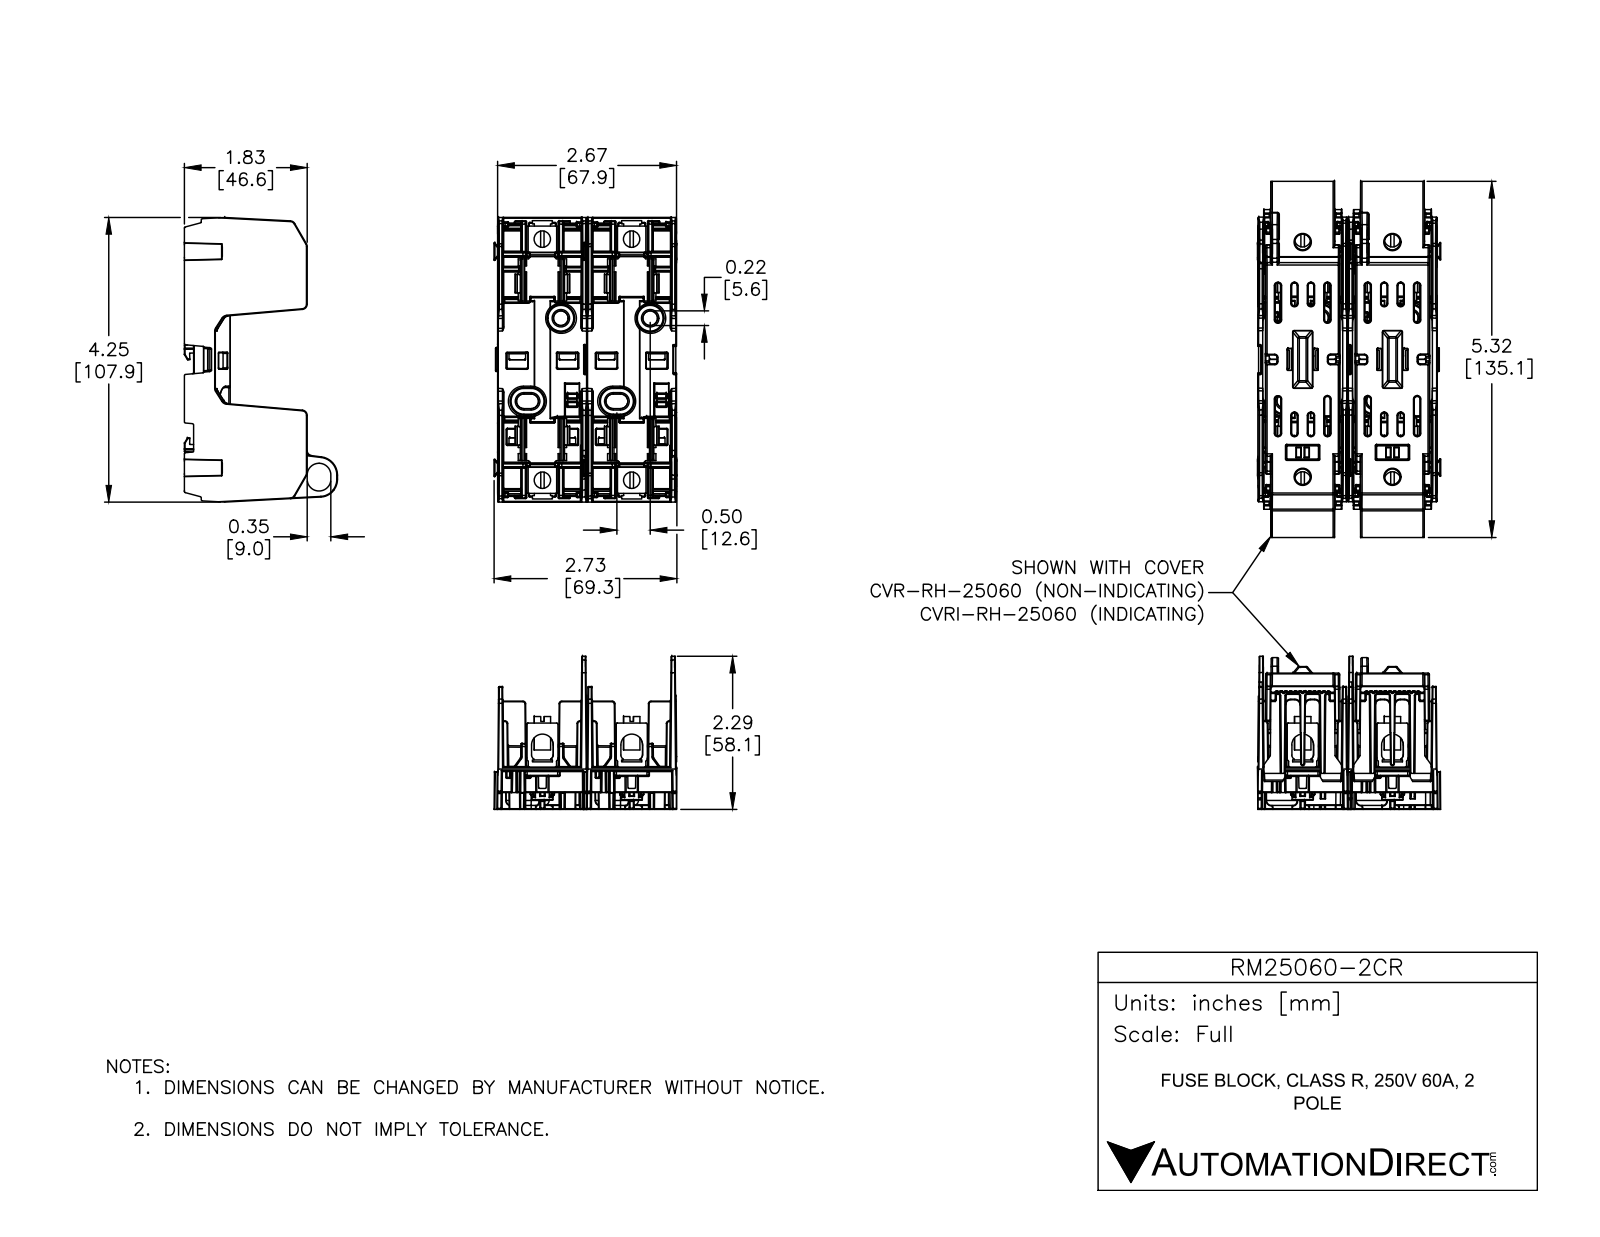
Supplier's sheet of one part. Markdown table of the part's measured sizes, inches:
| quantity | value |
| --- | --- |
| part name | RM25060-1CR; RM25060-2CR |
| STEP written by | SolidWorks 2016 (AUTOMOTIVE_DESIGN) |
| units | inches |
| bodies | 26 solids, 788 faces (456 planar, 332 cylindrical, 0 other) |
| overall size | 4.154 × 2.415 × 1.061 |
| volume | 0.592 in³ |
| surface area | 33.38 in² |
| round holes (diameter × count) | 0.225 × 4, 0.244 × 4 |
| round bosses / shafts (diameter × count) | 0.244 × 4 |
| partial cylindrical surfaces (radius × count) | 0.01 × 52, 0.02 × 32, 0.039 × 20, 0.02 × 16, 0.059 × 12, 0.07 × 8, 0.079 × 8, 0.087 × 8 |
| main face-to-face distances | 1.339, 0.028, 0.024, 0.054, 1.337, 0.051, 1.346, 1.331, 1.337, 0.078 |
| hole center spacings | 1.339, 0.582, 0.583, 1.459, 1.46, 2.435, 2.778, 3.017 |
